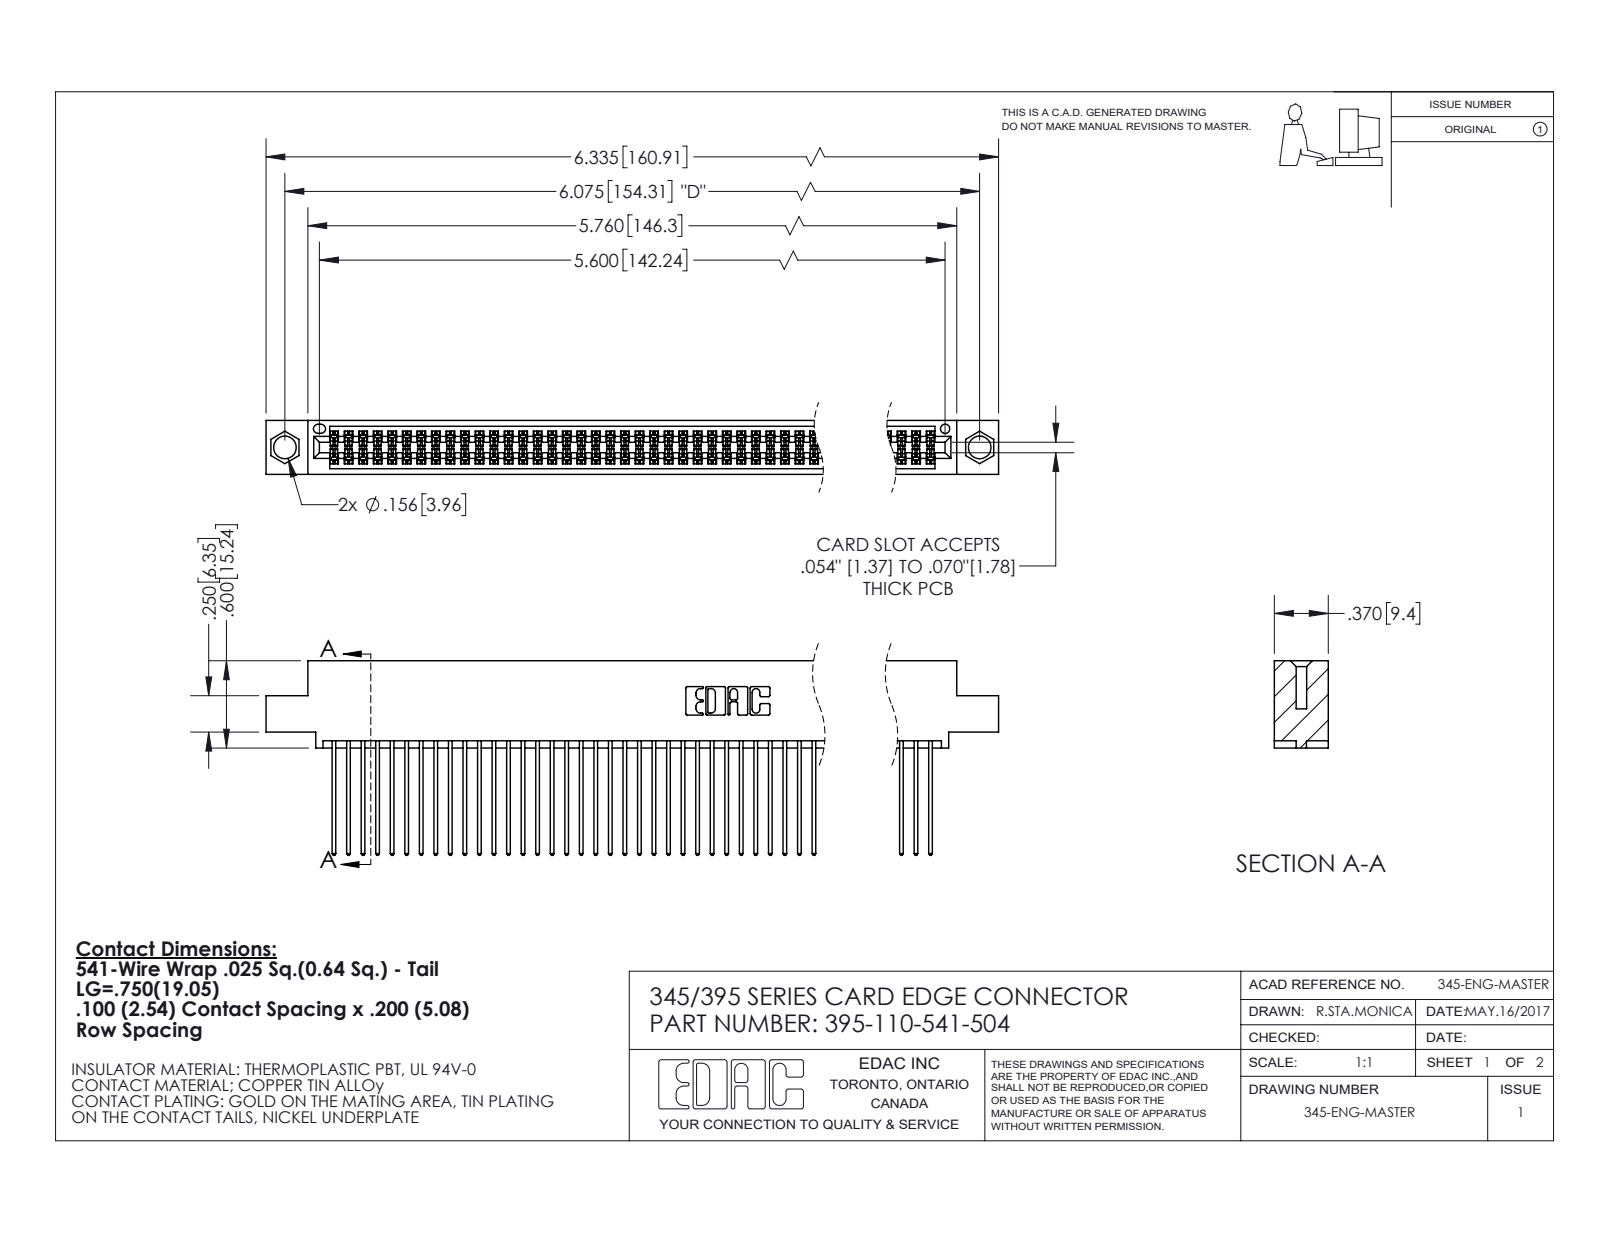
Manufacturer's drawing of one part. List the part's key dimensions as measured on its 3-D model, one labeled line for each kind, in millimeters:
Part name (STEP PRODUCT): 345 Part_0.110 Offset - 0.156 Dia-TI; 395-110-541-504; 345-292-001_345-293-141
STEP written by: SolidWorks 2020 (CONFIG_CONTROL_DESIGN)
Units: millimetres
Bodies: 111 solids, 5644 faces (3728 planar, 1916 cylindrical, 0 other)
Overall size (bounding box): 160.9 × 34 × 9.4
Volume: 16 200 mm³ · Surface area: 27 120 mm²
Round holes (diameter × count): ⌀4 ×2, ⌀1.6 ×1
Partial cylindrical surfaces — rounded edges, fillets, slot ends (radius × count): R0.2 ×220, R0.3 ×110, R0.3 ×22, R0.2 ×6, R0.8 ×6, R0.7 ×3, R0.4 ×2, R0.5 ×2
Main face-to-face distances: 7.6, 1.8, 5.1, 2.5, 6.9, 0.6, 5.7, 9.4, 4.4, 3.8
Hole centre spacings: 6.9, 148.3, 154.3
